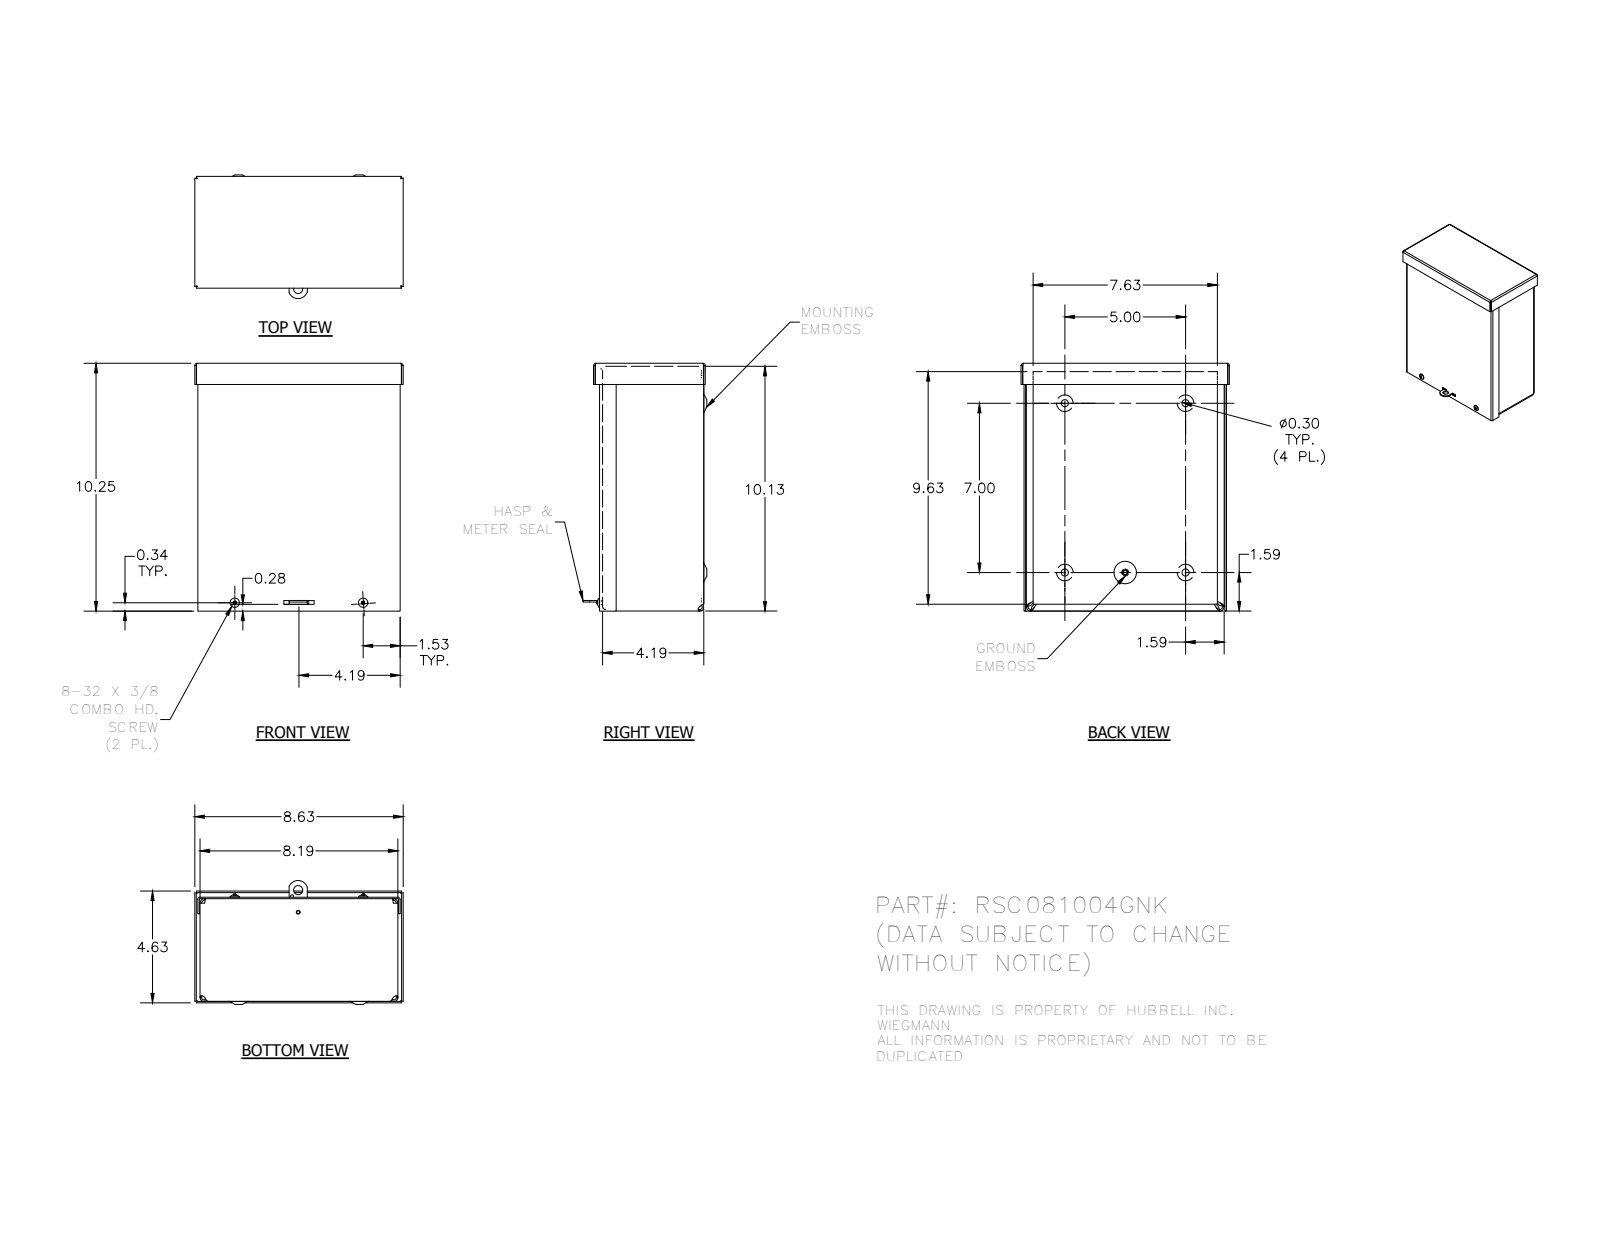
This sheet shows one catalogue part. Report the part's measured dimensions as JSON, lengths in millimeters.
{"part_name": "RSC081004GNK_WRAP; RSC0810GNK_LID; RSC0804GNK_CAP; 3183 (+3 more)", "step_written_by": "Autodesk Inventor 2014 (AUTOMOTIVE_DESIGN)", "units": "millimeters", "bodies": {"solids": 7, "faces": 377, "planar": 163, "cylindrical": 78, "other": 136}, "overall_size": [260.36, 219.07, 130.17], "volume_mm3": 438689, "surface_area_mm2": 565579, "round_holes": [[7.62, 4], [7.95, 4], [3.17, 2], [3.76, 2], [3.96, 1], [4.19, 1], [9.52, 1]], "round_bosses_or_shafts": [[9.75, 2], [4.17, 2], [5.8, 1]], "partial_cylinders_radius": [[0.79, 8], [2.37, 8], [3.17, 8], [4.75, 8], [1.4, 4], [1.57, 4], [2.38, 4], [2.97, 4]], "face_to_face_distances": [1.58, 1.57, 107.93, 106.35, 206.39, 1.59, 109.52, 107.94, 257.19, 3.15], "hole_center_spacings": [27.24, 32.03, 63.5, 127, 134.95, 177.8, 188.79, 204.79]}
